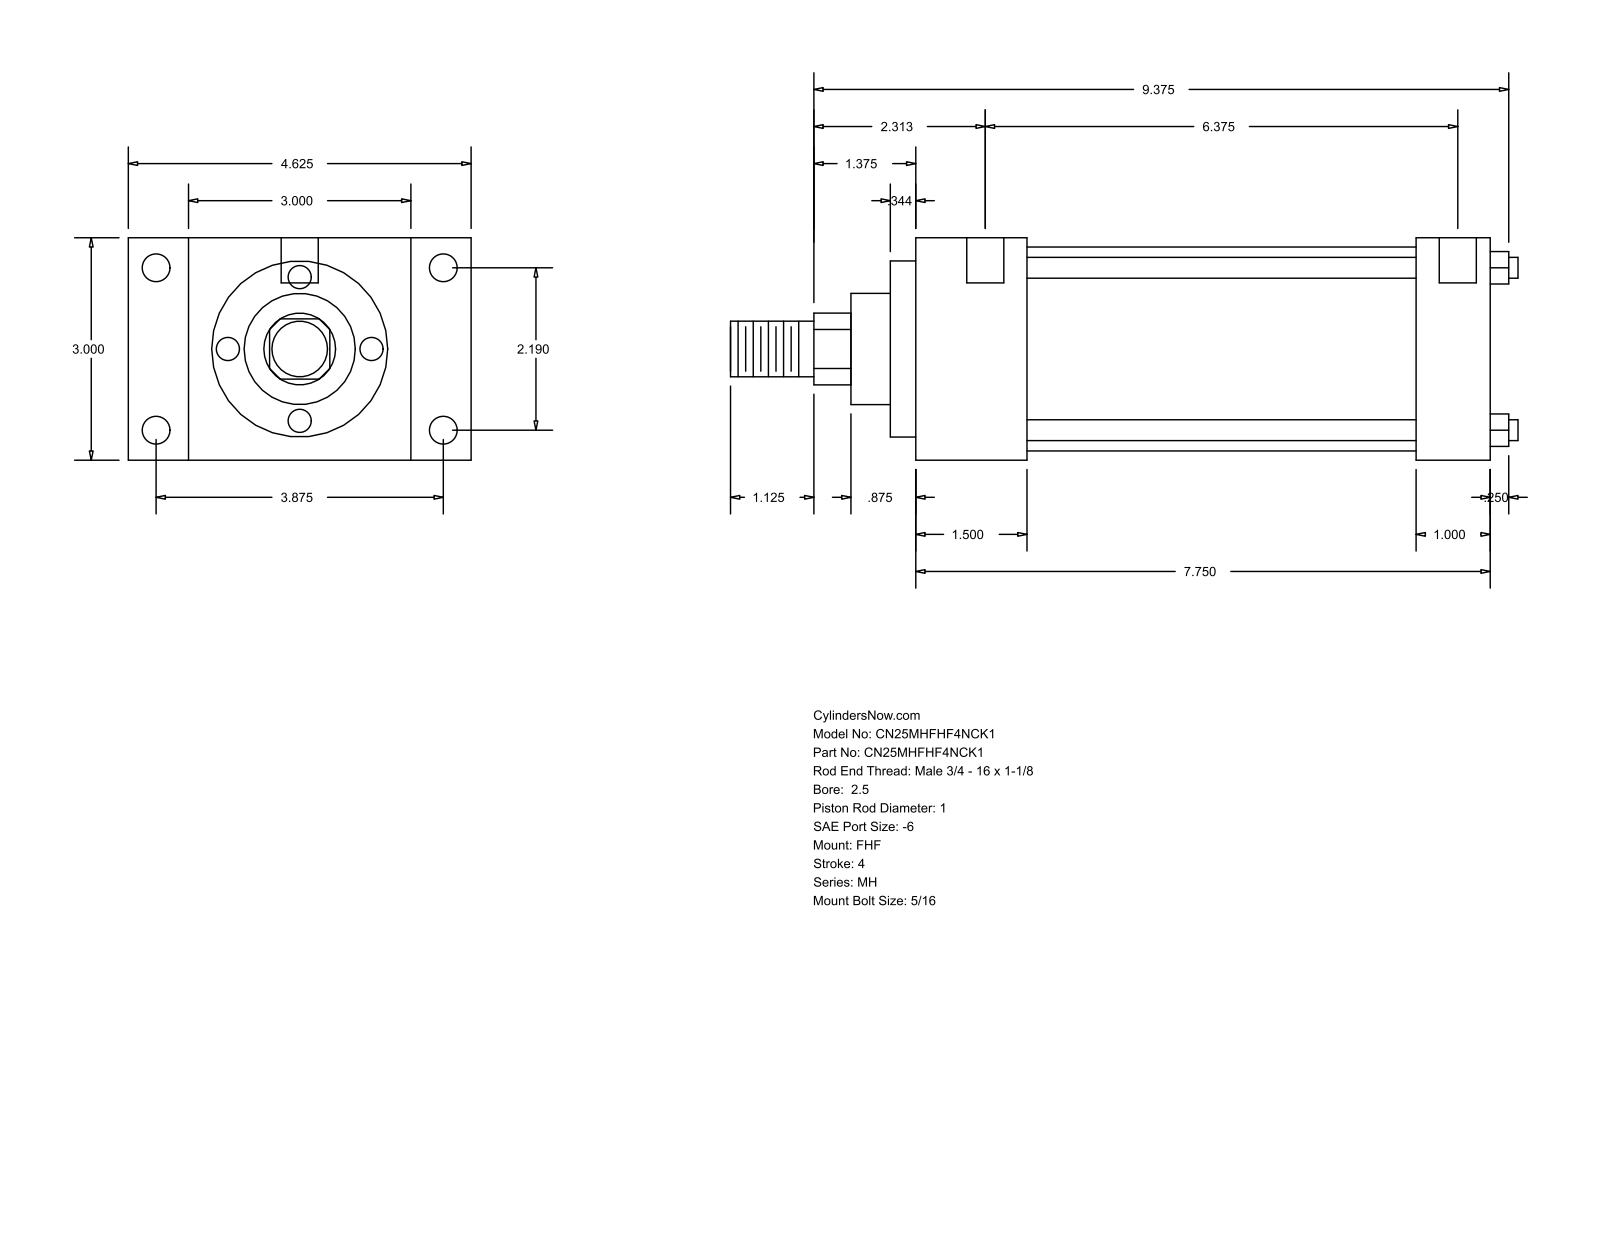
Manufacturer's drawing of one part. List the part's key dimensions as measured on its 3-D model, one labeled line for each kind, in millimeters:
Part name (STEP PRODUCT): MH_FHF__0250_1
STEP written by: GSSL Pune (CONFIG_CONTROL_DESIGN)
Units: millimetres
Bodies: 0 solids, 90 faces (61 planar, 29 cylindrical, 0 other)
Overall size (bounding box): 269.88 × 117.47 × 76.2
Round holes (diameter × count): ⌀5.56 ×4, ⌀9.53 ×4, ⌀12.7 ×2
Round bosses / shafts (diameter × count): ⌀7.14 ×4, ⌀69.85 ×1, ⌀60.33 ×1, ⌀38.1 ×1, ⌀25.4 ×1, ⌀19.05 ×1
Partial cylindrical surfaces — rounded edges, fillets, slot ends (radius × count): R12.29 ×1
Main face-to-face distances: 76.2, 196.86, 38.11, 158.75, 20.64, 96.84, 117.48, 171.46, 133.35, 25.4
Hole centre spacings: 55.62, 98.42, 113.05, 169.86, 3.18, 4.76, 161.92, 165.1
